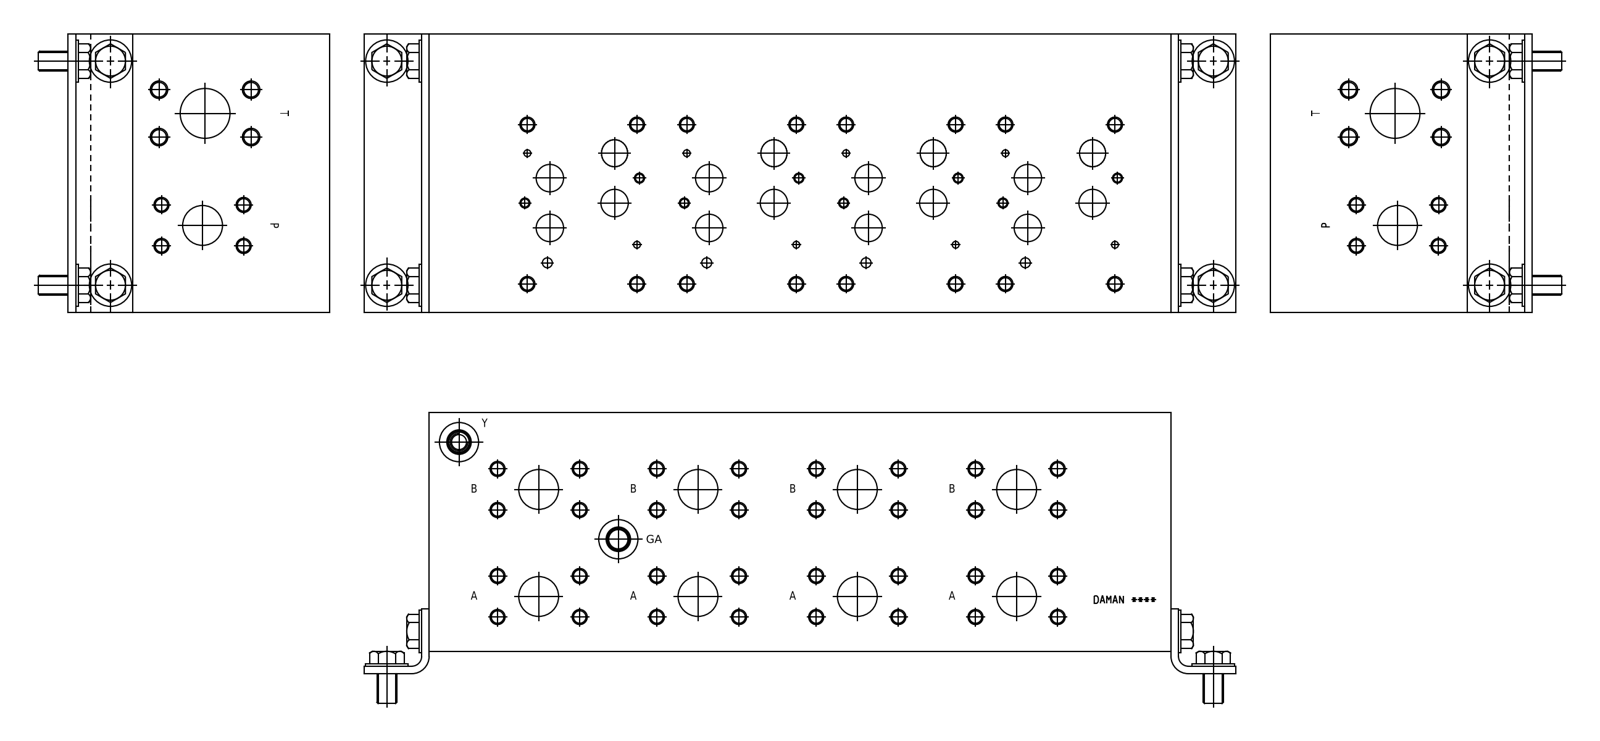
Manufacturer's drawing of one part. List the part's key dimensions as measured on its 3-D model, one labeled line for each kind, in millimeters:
Part name (STEP PRODUCT): C:\\Program Files\\PARO\\Hydroman 800\\Export\\AD07HP044F
STEP written by: Autodesk Inventor 2012 (AUTOMOTIVE_DESIGN)
Units: millimetres
Bodies: 1 solid, 410 faces (88 planar, 202 cylindrical, 120 other)
Overall size (bounding box): 473.07 × 177.8 × 152.4
Volume: 12 560 000 mm³ · Surface area: 449 579 mm²
Round holes (diameter × count): ⌀9.53 ×57, ⌀7.92 ×56, ⌀6.35 ×12, ⌀17.48 ×12, ⌀25.4 ×9, ⌀4.37 ×8, ⌀5.11 ×8, ⌀9.35 ×4, ⌀11.11 ×4, ⌀16.66 ×4, ⌀10.72 ×2, ⌀12.7 ×2
Main face-to-face distances: 152.4, 177.8, 473.08, 25.4, 0.76, 24.64, 177.04, 127, 3.17, 447.68
Hole centre spacings: 101.6, 26.17, 52.38, 58.55, 104.92, 29.27, 76.54, 203.2
